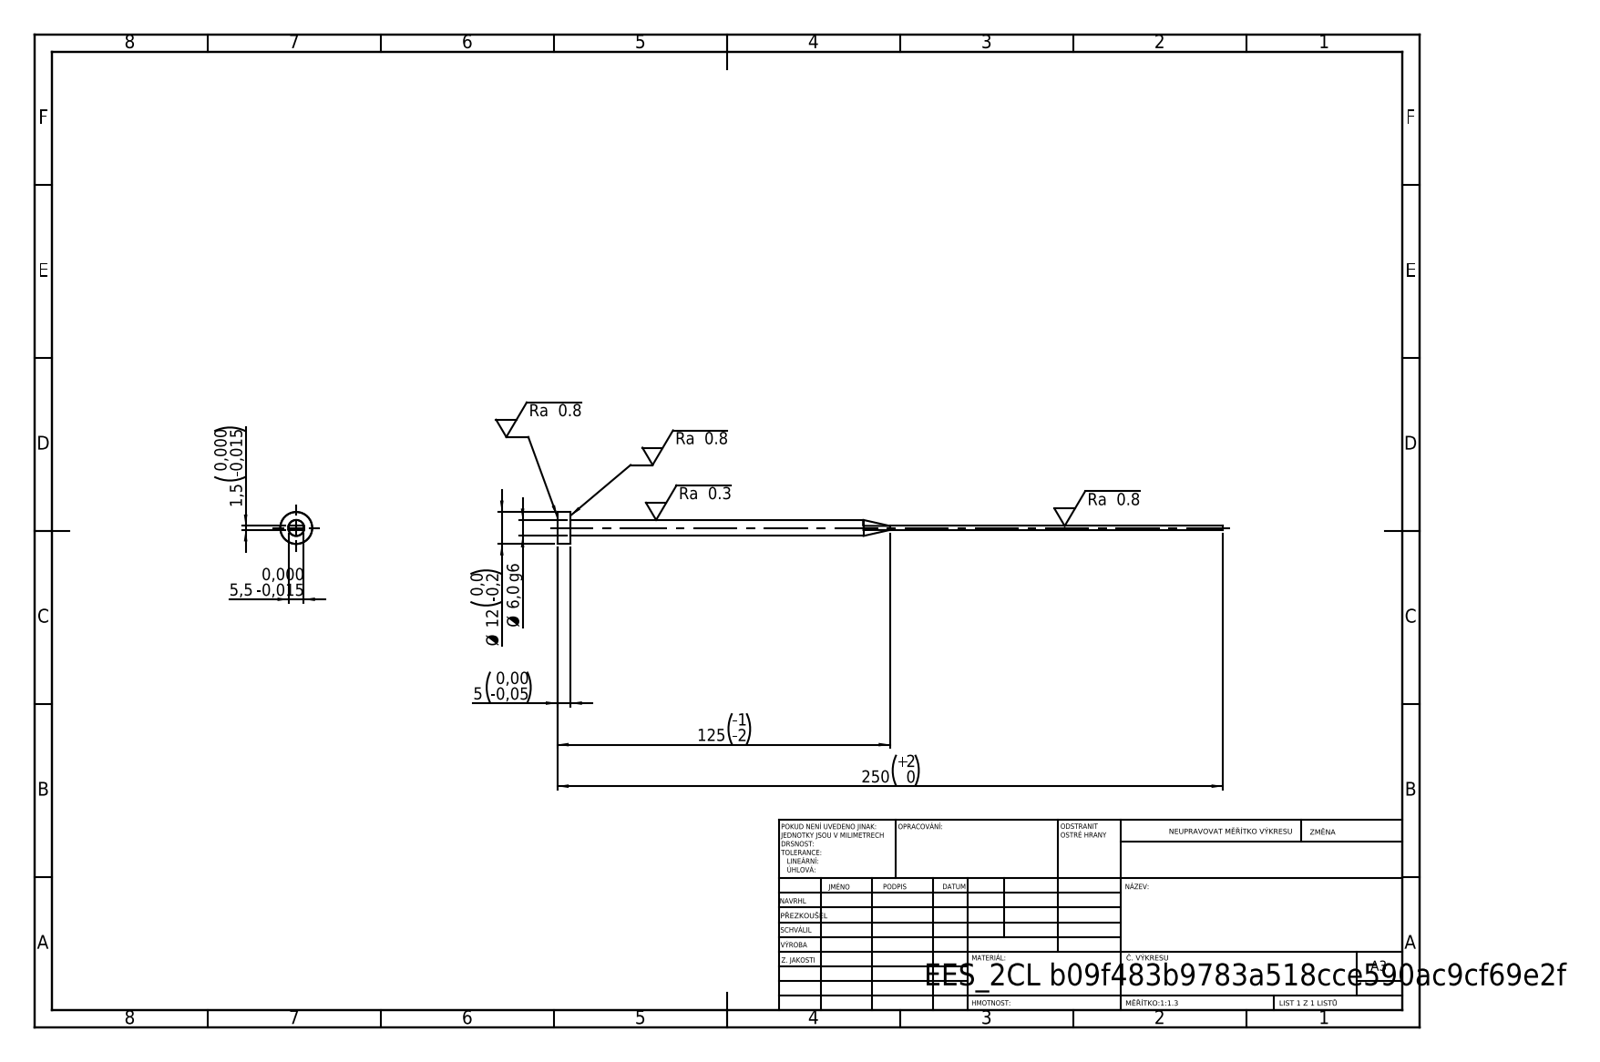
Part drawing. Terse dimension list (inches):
written by: SolidWorks 2019 (CONFIG_CONTROL_DESIGN)
unit: in
bodies: 1 solid, 15 faces (7 planar, 4 cylindrical, 4 other)
size: 9.843 × 0.472 × 0.472
volume: 0.298 in³; area: 6.786 in²
bosses: 1× ⌀0.472, 1× ⌀0.236
face distances: 0.059, 0.217, 0.197, 9.843, 9.646
